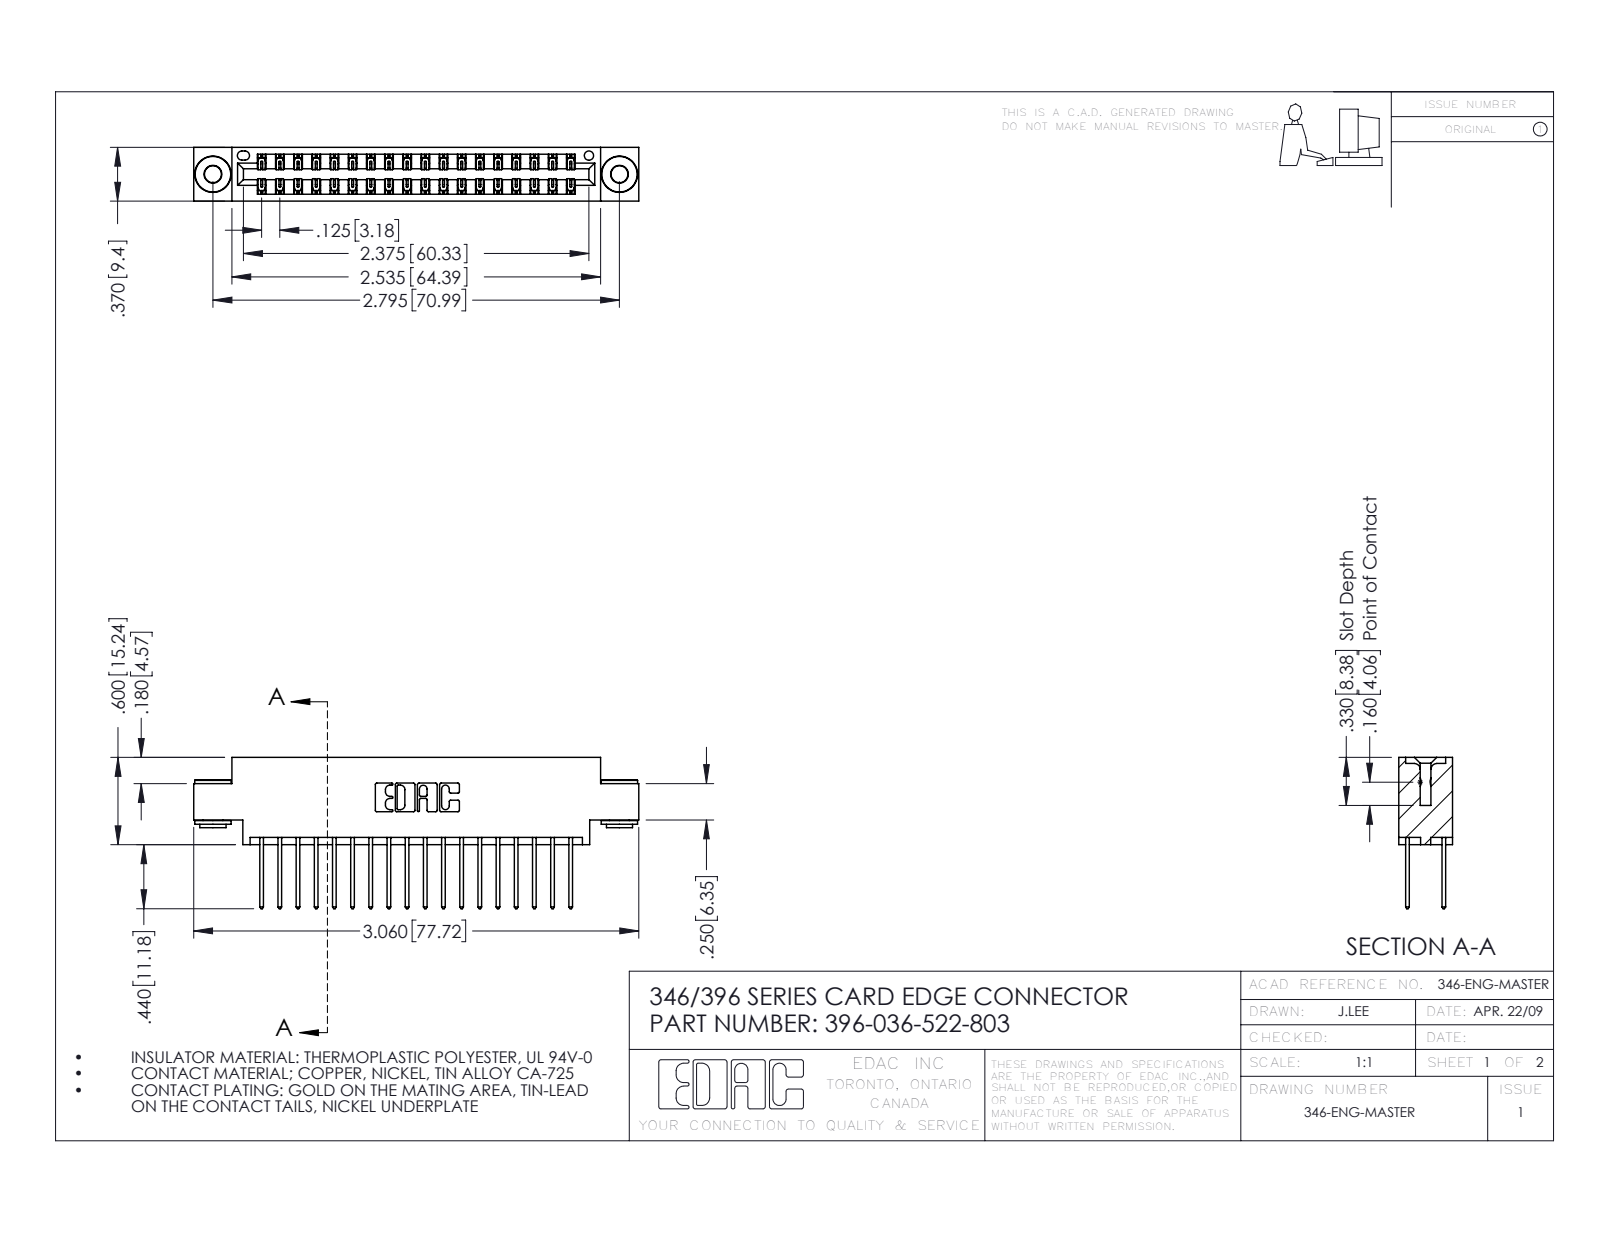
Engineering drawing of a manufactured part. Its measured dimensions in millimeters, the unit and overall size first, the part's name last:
Units: millimetres
Overall size (bounding box): 77.7 × 26.4 × 9.4
Round holes (diameter × count): ⌀2.9 ×2, ⌀4 ×2, ⌀1.6 ×1
Round bosses / shafts (diameter × count): ⌀6.4 ×2, ⌀4.6 ×2, ⌀3.5 ×2
Partial cylindrical surfaces — rounded edges, fillets, slot ends (radius × count): R0.2 ×54, R0.3 ×36, R0.3 ×22, R0.2 ×6, R0.8 ×6, R0.7 ×3, R0.4 ×2, R0.6 ×2
Main face-to-face distances: 1.2, 8.2, 6.4, 9.4, 0.6, 1.8, 7.6, 7, 3.8, 5.6
Hole centre spacings: 6.2, 65.7, 71
Volume: 7 360 mm³ · Surface area: 10 550 mm²
Bodies: 39 solids, 2036 faces (1350 planar, 678 cylindrical, 8 other)
Part name (STEP PRODUCT): 346 Part_0.170 Offset - 0.156 Dia-TH; 345-250-002_345-250-002-102; 396-036-522-803; 345-292-001_345-293-122
STEP written by: SolidWorks 2016 (CONFIG_CONTROL_DESIGN)
